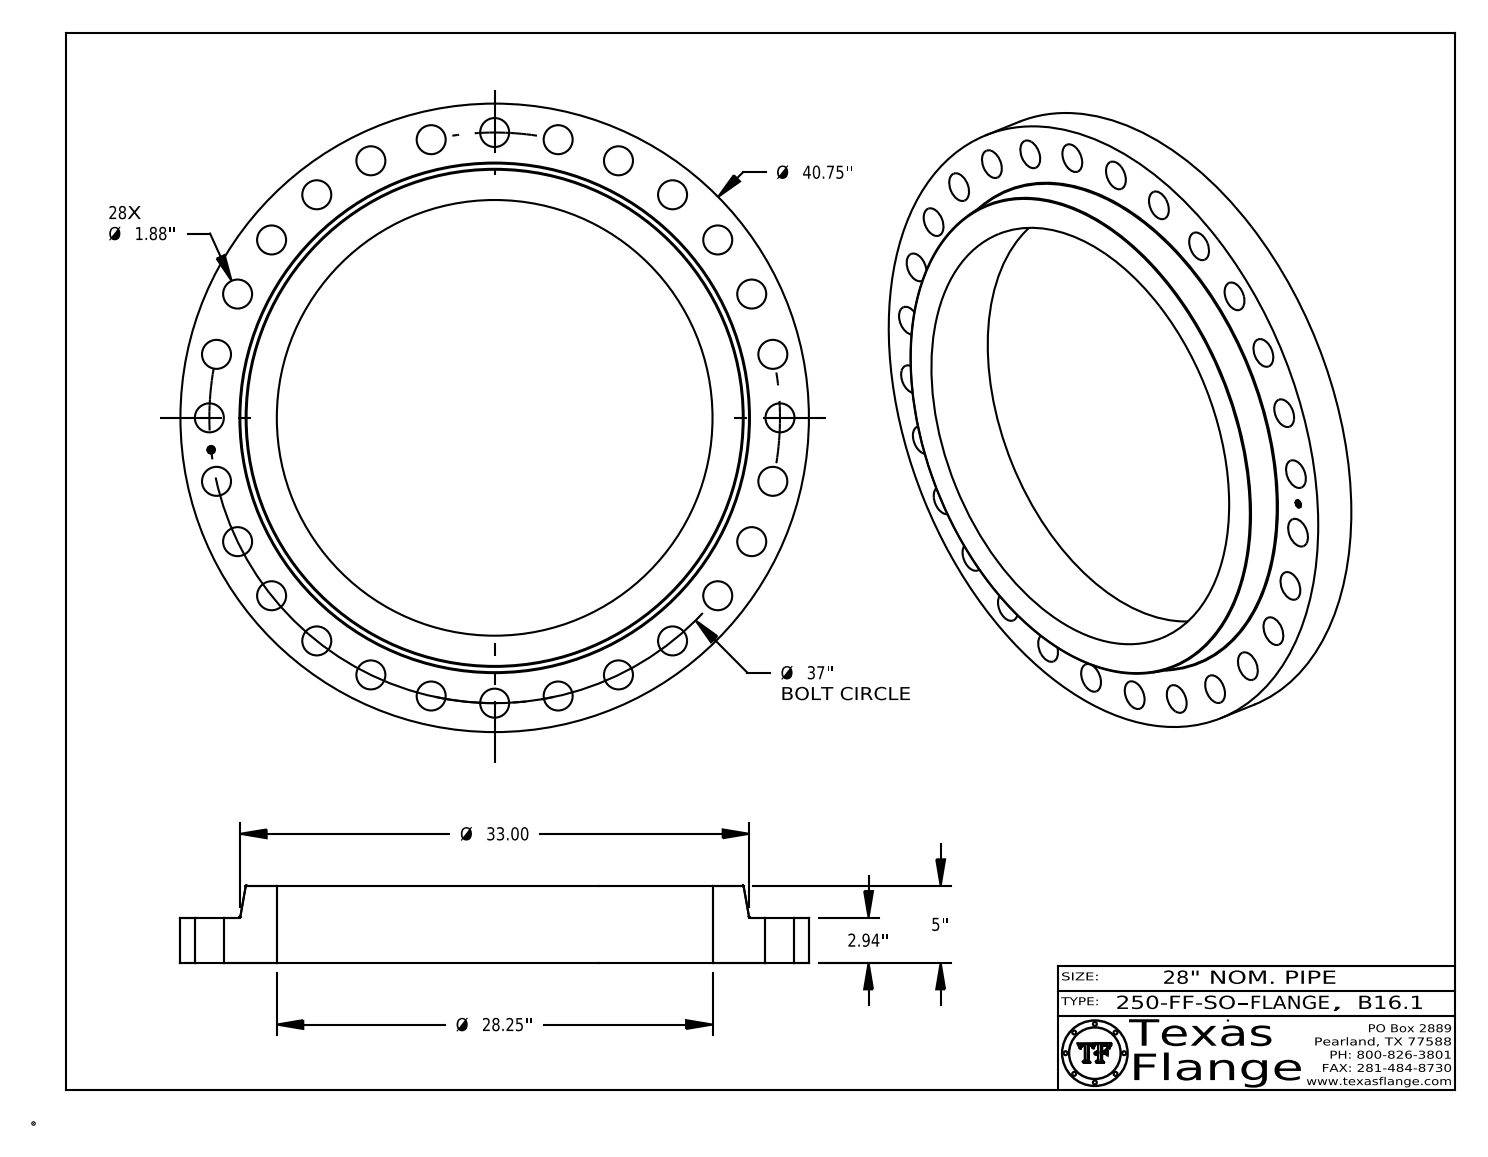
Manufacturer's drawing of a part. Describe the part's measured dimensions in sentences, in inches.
The part is named "B16.1, Class 250-FF-SO". Its 3-D file was written by "CATIA V5 STEP AP214 (AUTOMOTIVE_DESIGN)". It is 1 solid with 454 faces: 368 planar, 80 cylindrical and 6 other. Overall it measures 40.75 by 40.75 by 5 inches. Its volume is 2 195 cubic inches and its surface area 2 680 square inches. Round holes: 28 of diameter 1.88, 1 of diameter 0.495, 1 of diameter 28.25. Round bosses or shafts: 8 of diameter 0.03, 1 of diameter 40.75, 1 of diameter 0.39. The main face-to-face distances are 2.94, 5, 2.06, 2.925, 0.015, 2.075, 0.148, 0.144, 0.027, 0.096. The hole center spacings are 18.5, 26.163, 31.329, 36.072, 36.767, 33.336, 4.143, 16.054.
